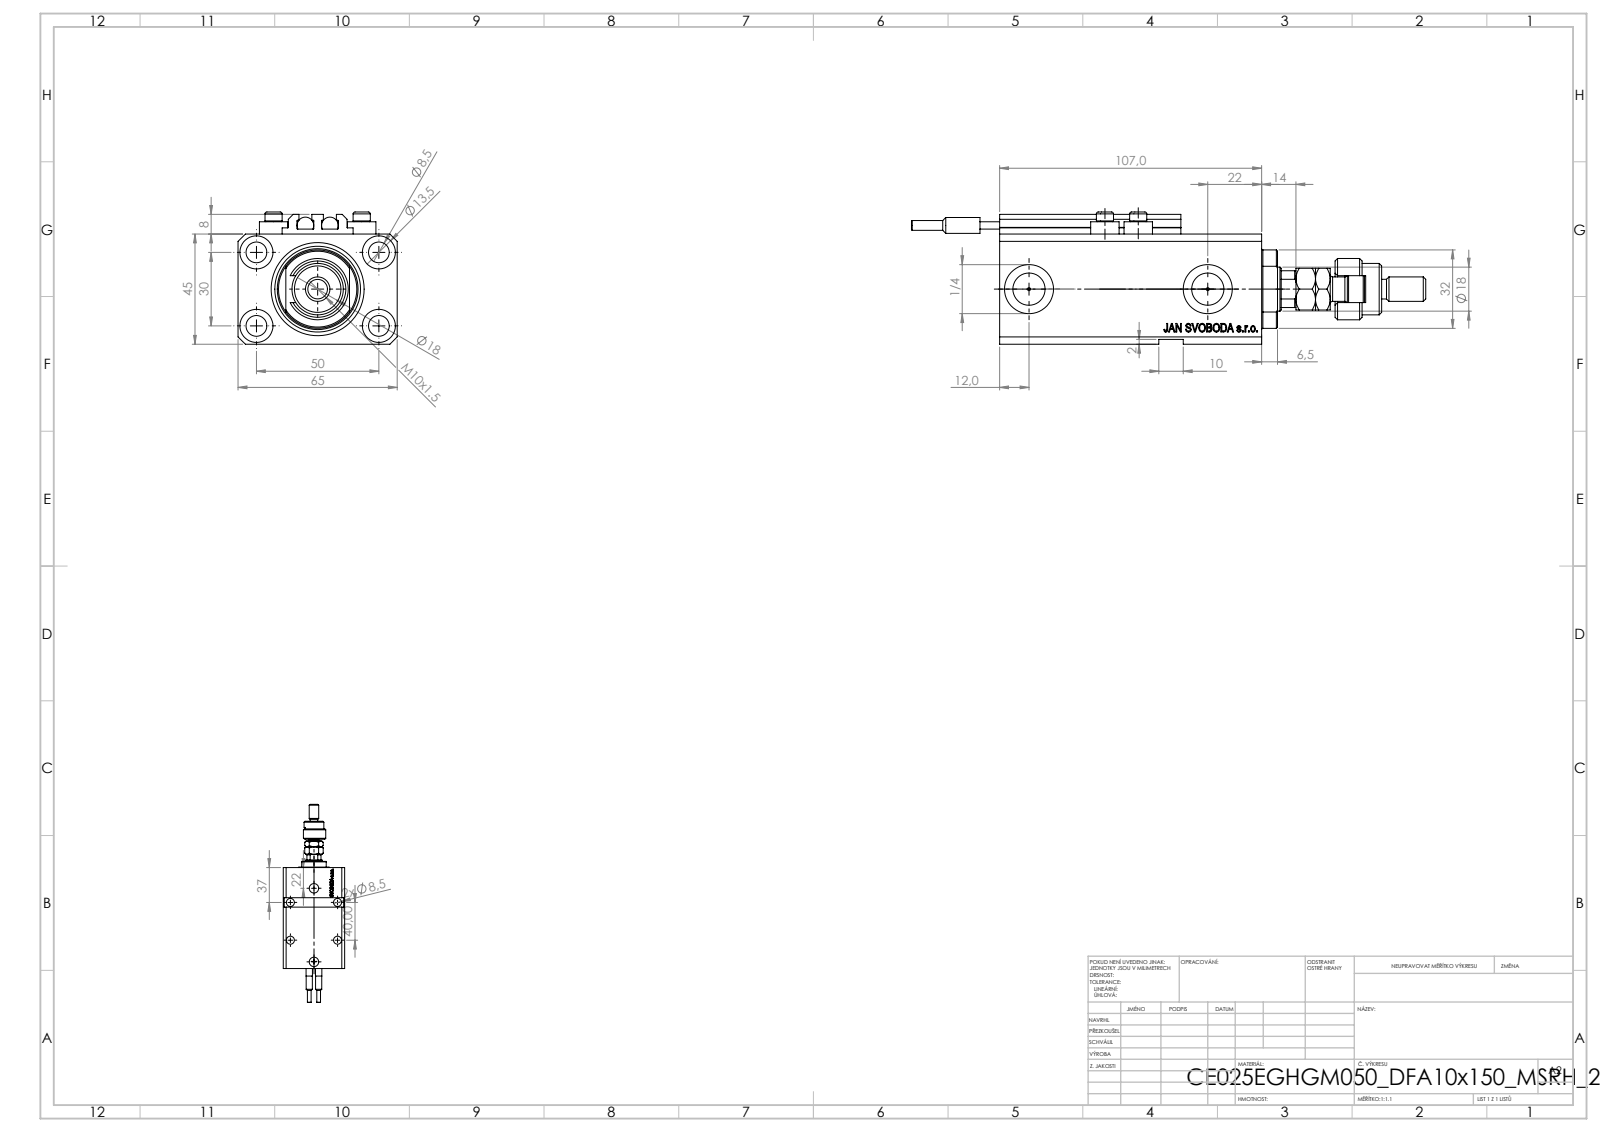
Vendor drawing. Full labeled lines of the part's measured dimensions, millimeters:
Part name (STEP PRODUCT): MFA; V250CE_VC_E; ALLEN BOLT V250CE; FEMALE_PART_FOR_DFA (+3 more)
STEP written by: SolidWorks 2019 (CONFIG_CONTROL_DESIGN)
Units: millimetres
Bodies: 12 solids, 1224 faces (571 planar, 171 cylindrical, 482 other)
Overall size (bounding box): 210 × 65 × 54
Volume: 288 767 mm³ · Surface area: 85 071 mm²
Round holes (diameter × count): ⌀8.5 ×9, ⌀1.25 ×4, ⌀4 ×4, ⌀13.5 ×4, ⌀10 ×2, ⌀13.16 ×2, ⌀20 ×2, ⌀18 ×1, ⌀38 ×1
Round bosses / shafts (diameter × count): ⌀11.6 ×4, ⌀7 ×4, ⌀6.8 ×2, ⌀6.5 ×2, ⌀4 ×2, ⌀25 ×1, ⌀21 ×1, ⌀16 ×1
Partial cylindrical surfaces — rounded edges, fillets, slot ends (radius × count): R0.2 ×10, R5.5 ×1, R8.5 ×1, R8.75 ×1, R16 ×1
Main face-to-face distances: 45, 65, 14, 2, 47, 3, 93, 107, 5, 10
Hole centre spacings: 29.15, 50, 13.6, 14.76, 15.12, 27.51, 27.89, 30
